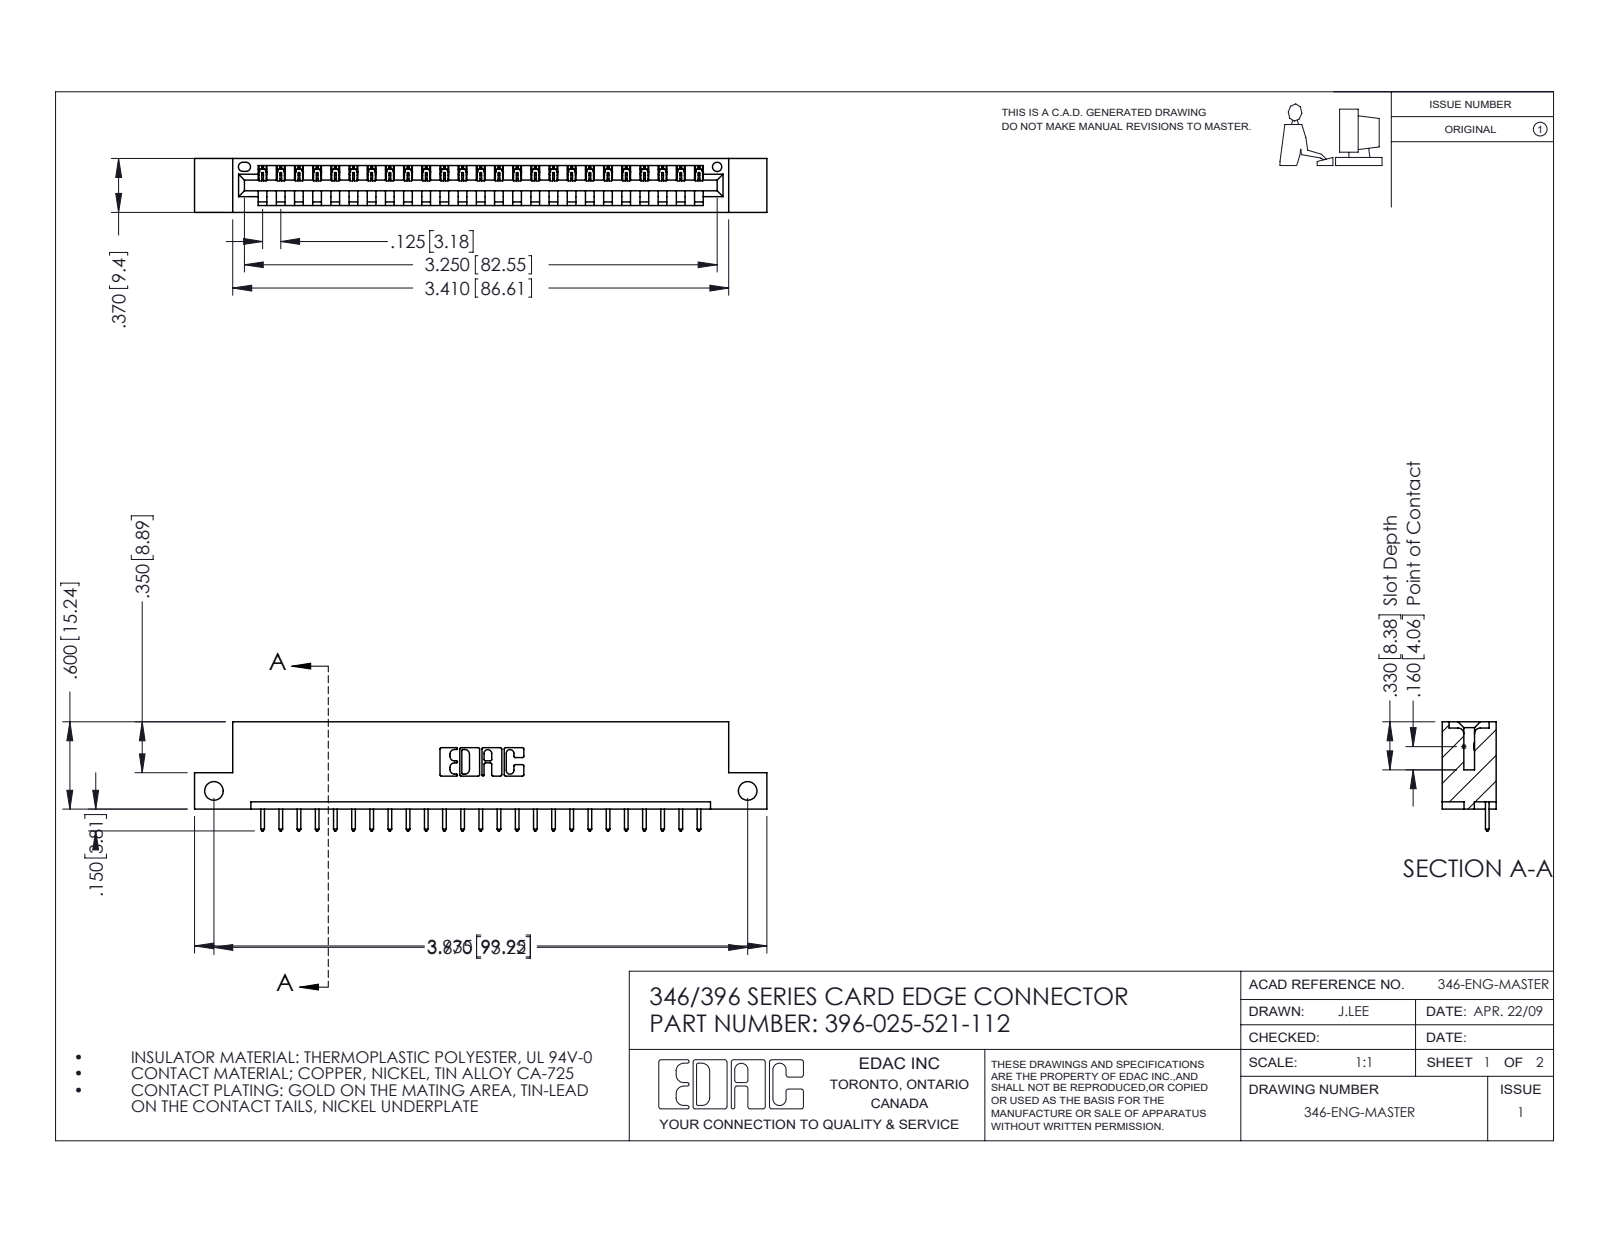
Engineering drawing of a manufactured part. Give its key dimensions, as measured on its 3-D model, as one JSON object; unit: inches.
{"part_name": "346 Part_Flush Mounting Lugs - Side Mount; 345-292-001_345-293-121; 396-025-521-112", "step_written_by": "SolidWorks 2016 (CONFIG_CONTROL_DESIGN)", "units": "inches", "bodies": {"solids": 26, "faces": 1572, "planar": 1076, "cylindrical": 496, "other": 0}, "overall_size": [3.935, 0.75, 0.37], "volume_in3": 0.567, "surface_area_in2": 17.05, "round_holes": [[0.128, 2], [0.064, 1]], "partial_cylinders_radius": [[0.006, 50], [0.01, 50], [0.01, 22], [0.007, 6], [0.031, 6], [0.026, 3], [0.031, 2], [0.04, 2]], "face_to_face_distances": [0.048, 0.322, 0.37, 0.25, 0.072, 0.298, 0.025, 0.148, 0.222, 0.1], "hole_center_spacings": [3.67]}
